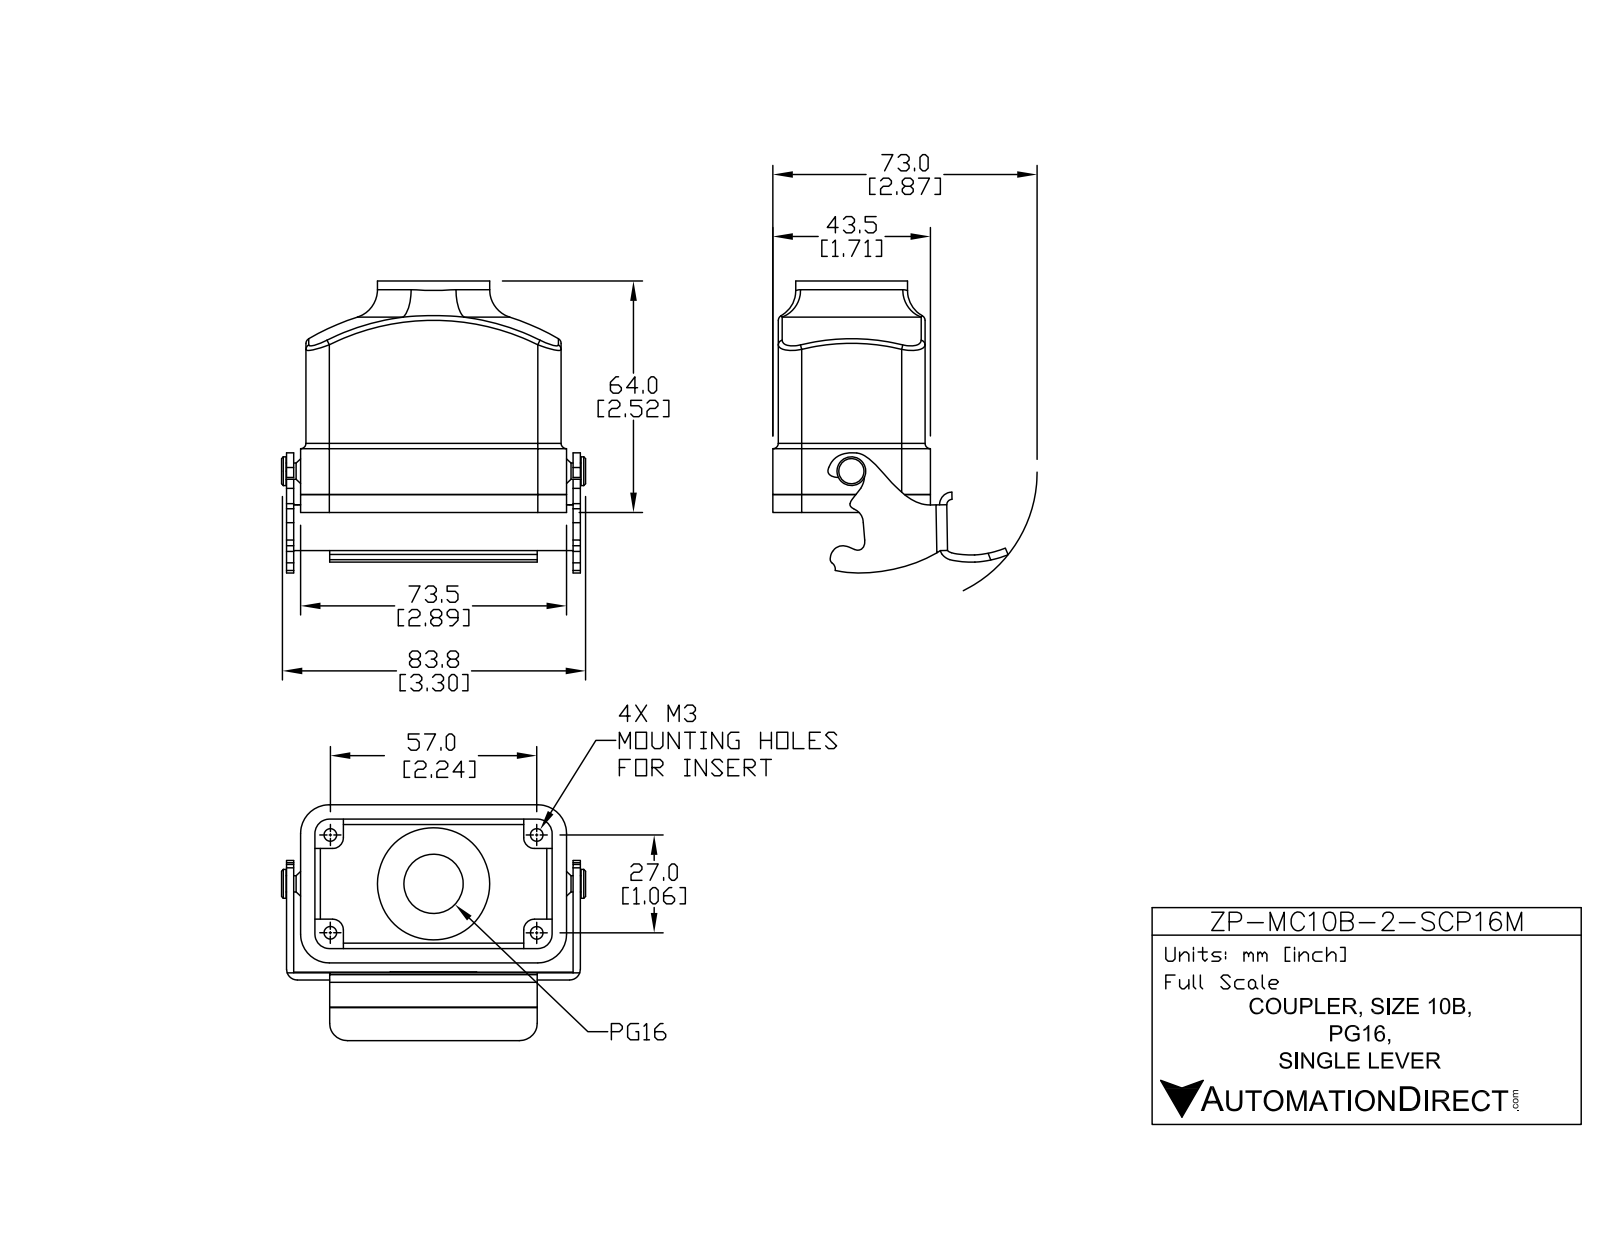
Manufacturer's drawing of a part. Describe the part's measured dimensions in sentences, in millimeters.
The part is named "ZP-MC10B-2-SCP16M". Its 3-D file was written by "SolidWorks 2011 (AUTOMOTIVE_DESIGN)". It is 5 solids with 219 faces: 80 planar, 106 cylindrical and 33 other. Overall it measures 86.5 by 70.19 by 64 millimeters. Its volume is 64 752 cubic millimeters and its surface area 39 336 square millimeters. Round holes: 4 of diameter 3.5, 1 of diameter 16.5, 1 of diameter 21. Round bosses or shafts: 1 of diameter 31.25, 1 of diameter 8, 1 of diameter 4.52. Partial cylindrical surfaces (rounded edges, fillets, slot ends): 14 of radius 0.5, 7 of radius 4, 5 of radius 3, 4 of radius 1.5, 4 of radius 5.5, 4 of radius 6.5, 4 of radius 8, 3 of radius 2. The main face-to-face distances are 4, 1.5, 38.5, 5.5, 37, 2.5, 1.15, 42.5, 41, 68.5. The hole center spacings are 30.88, 25.66, 56.18, 61.76.
